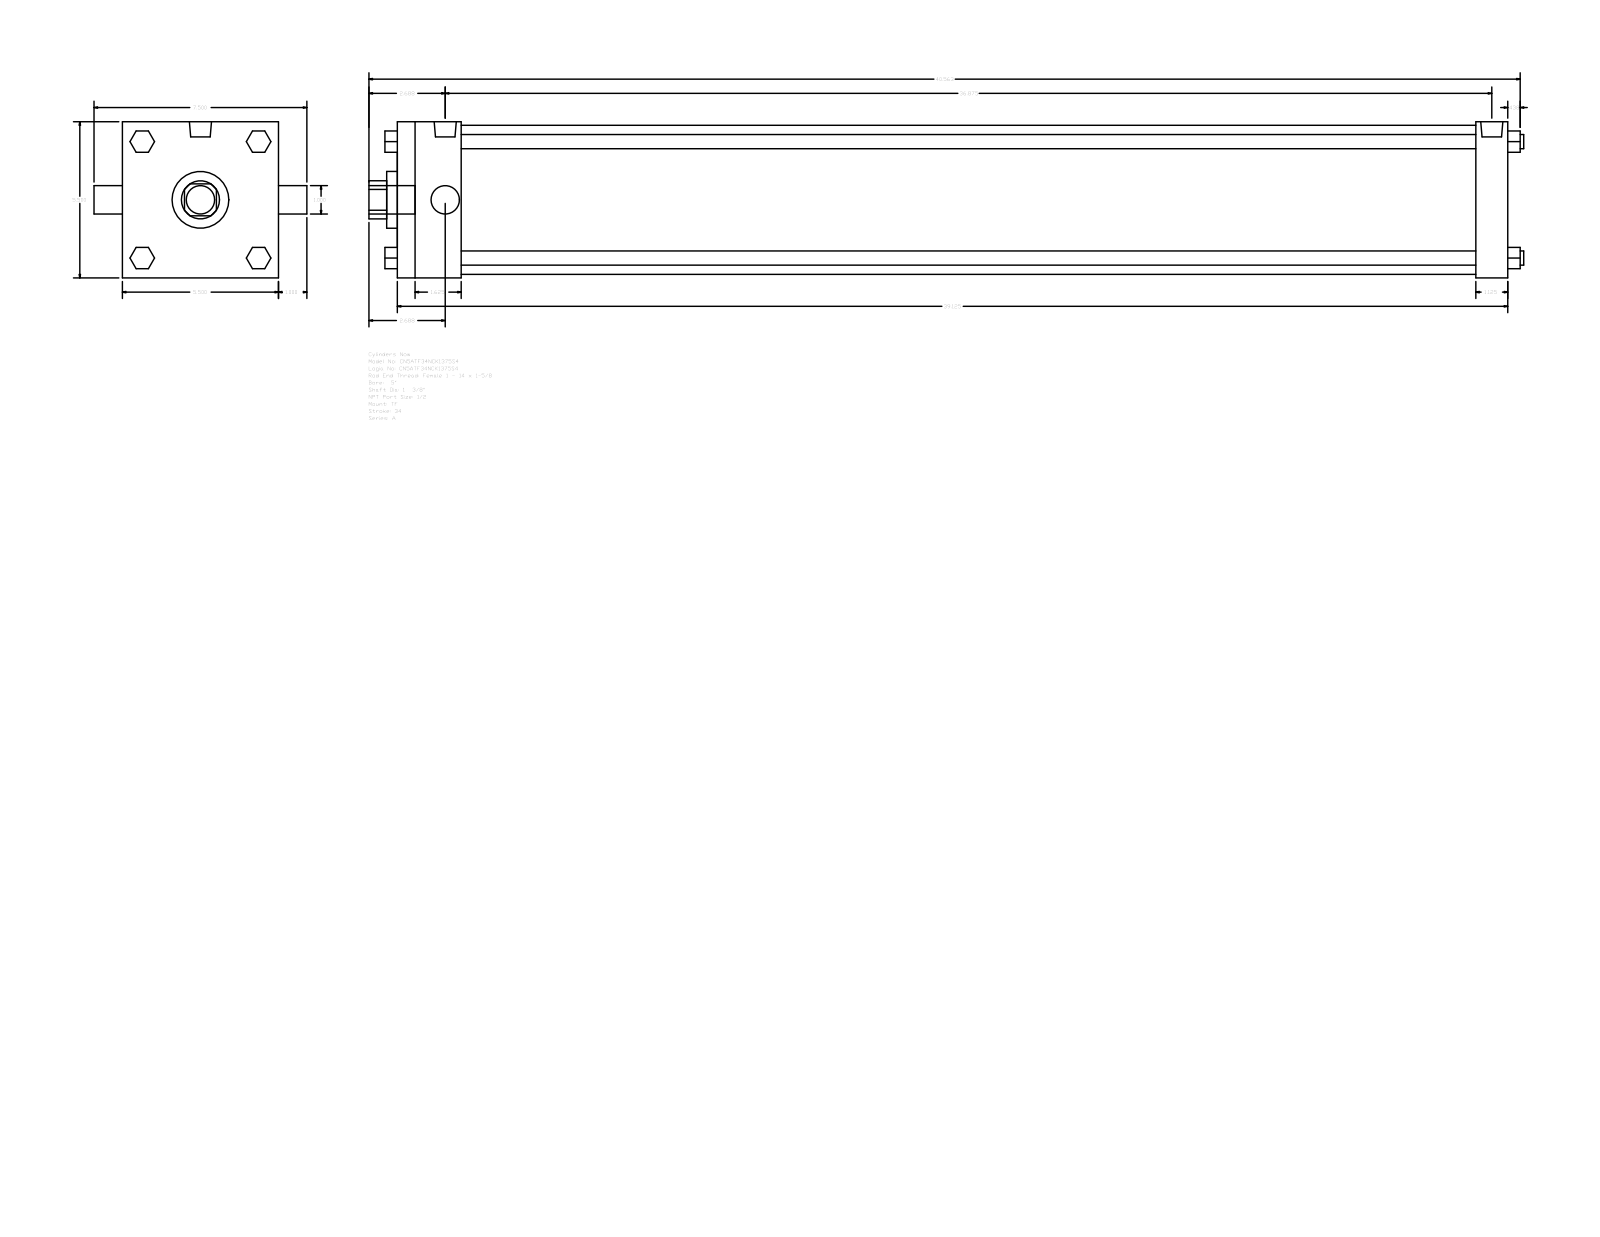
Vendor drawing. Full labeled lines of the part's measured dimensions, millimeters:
Part name (STEP PRODUCT): A_TF__0500_1.375
STEP written by: GSSL Pune (CONFIG_CONTROL_DESIGN)
Units: millimetres
Bodies: 0 solids, 120 faces (92 planar, 28 cylindrical, 0 other)
Overall size (bounding box): 1033.46 × 190.5 × 139.7
Round holes (diameter × count): ⌀25.4 ×1, ⌀34.92 ×1, ⌀50.8 ×1, ⌀133.35 ×1
Round bosses / shafts (diameter × count): ⌀12.7 ×4, ⌀8.73 ×3, ⌀19.77 ×2, ⌀25.4 ×1
Partial cylindrical surfaces — rounded edges, fillets, slot ends (radius × count): R17.06 ×1
Main face-to-face distances: 139.7, 993.77, 28.57, 965.2, 57.15, 908.05, 936.62, 19.05, 52.07, 90.18
